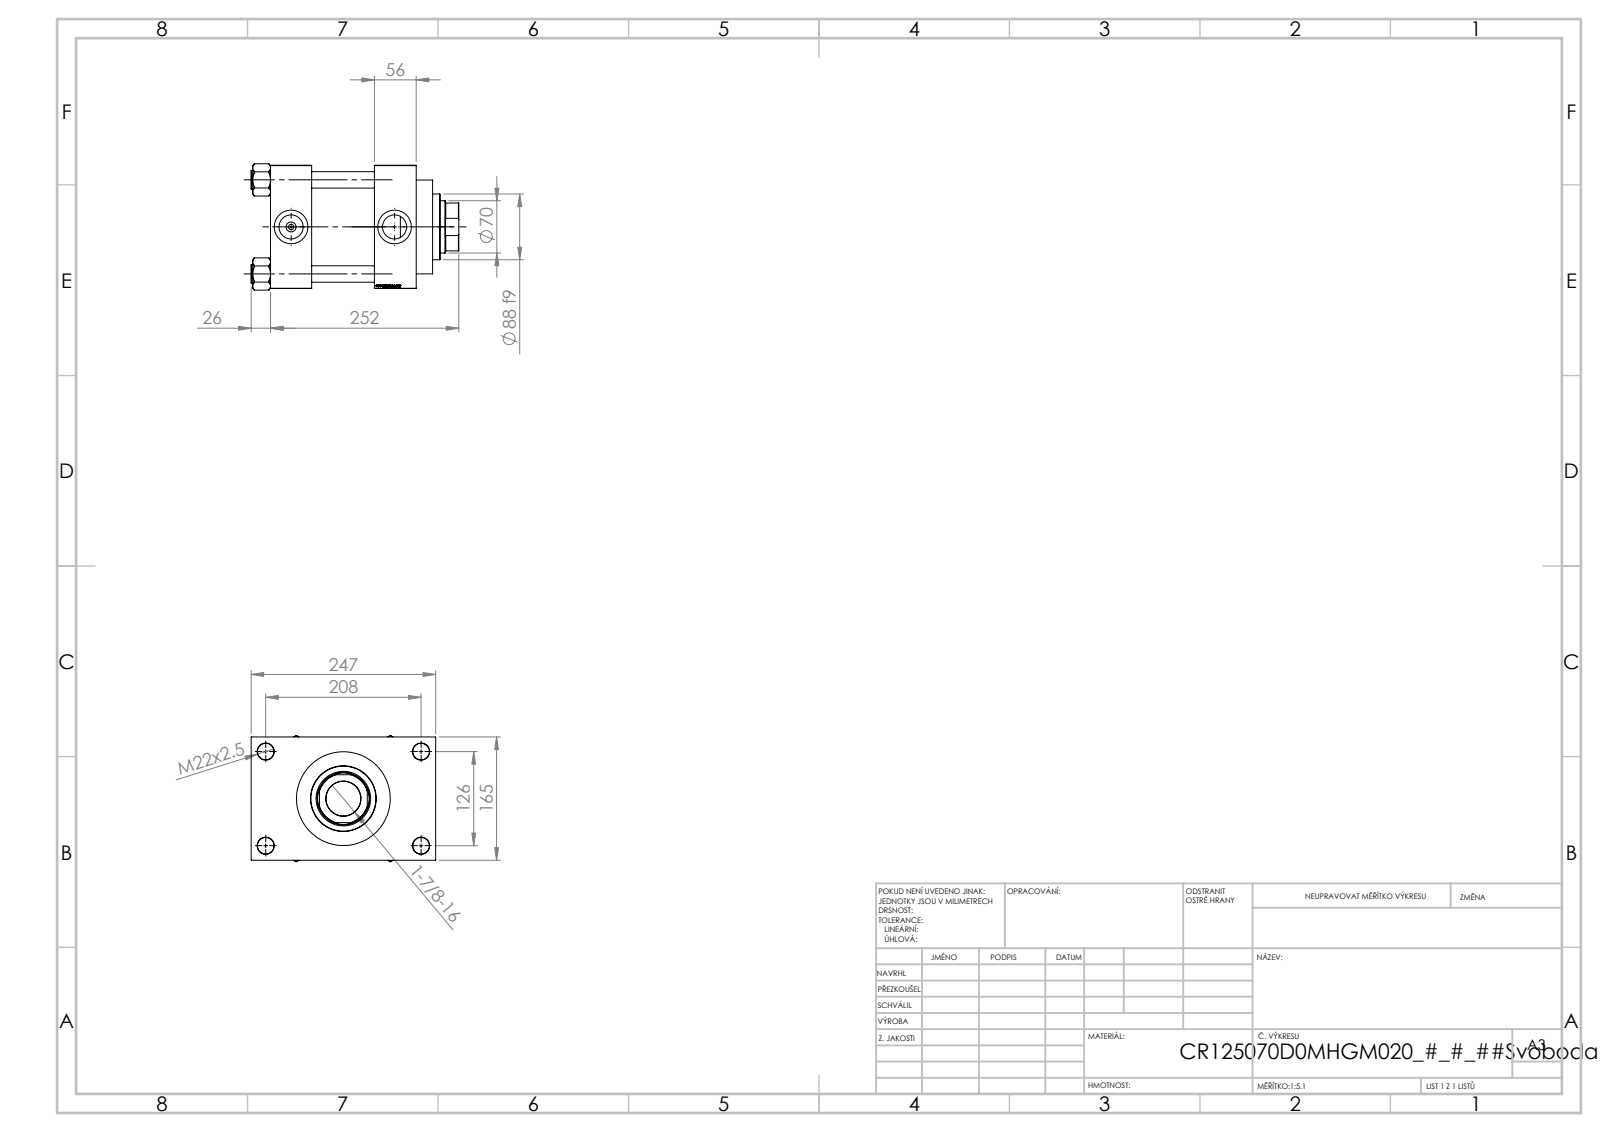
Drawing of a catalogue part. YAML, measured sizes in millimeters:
part_name: "V215_VC_A; V215CR_D_Body; NUT_M5_D; V215CR_VCP_D (+1 more)"
step_written_by: "SolidWorks 2019 (CONFIG_CONTROL_DESIGN)"
units: millimeters
bodies: {solids: 11, faces: 1148, planar: 544, cylindrical: 86, other: 518}
overall_size: [278, 247, 169.14]
volume: 5013000
surface_area: 542141
round_holes:
  - {diameter: 22, count: 8}
  - {diameter: 7, count: 2}
  - {diameter: 32.24, count: 2}
  - {diameter: 45, count: 2}
  - {diameter: 46.5, count: 1}
  - {diameter: 70, count: 1}
  - {diameter: 73, count: 1}
  - {diameter: 96, count: 1}
  - {diameter: 125, count: 1}
  - {diameter: 125.5, count: 1}
round_bosses_or_shafts:
  - {diameter: 25, count: 4}
  - {diameter: 131, count: 1}
  - {diameter: 88, count: 1}
partial_cylinders:
  - {radius: 34, count: 1}
face_to_face_distances: [165, 84, 55, 139, 195, 140, 56, 41, 206, 173.74]
hole_center_spacings: [41.05, 89.02, 121.59, 125.9, 132.47, 166.95, 209.13, 126]
